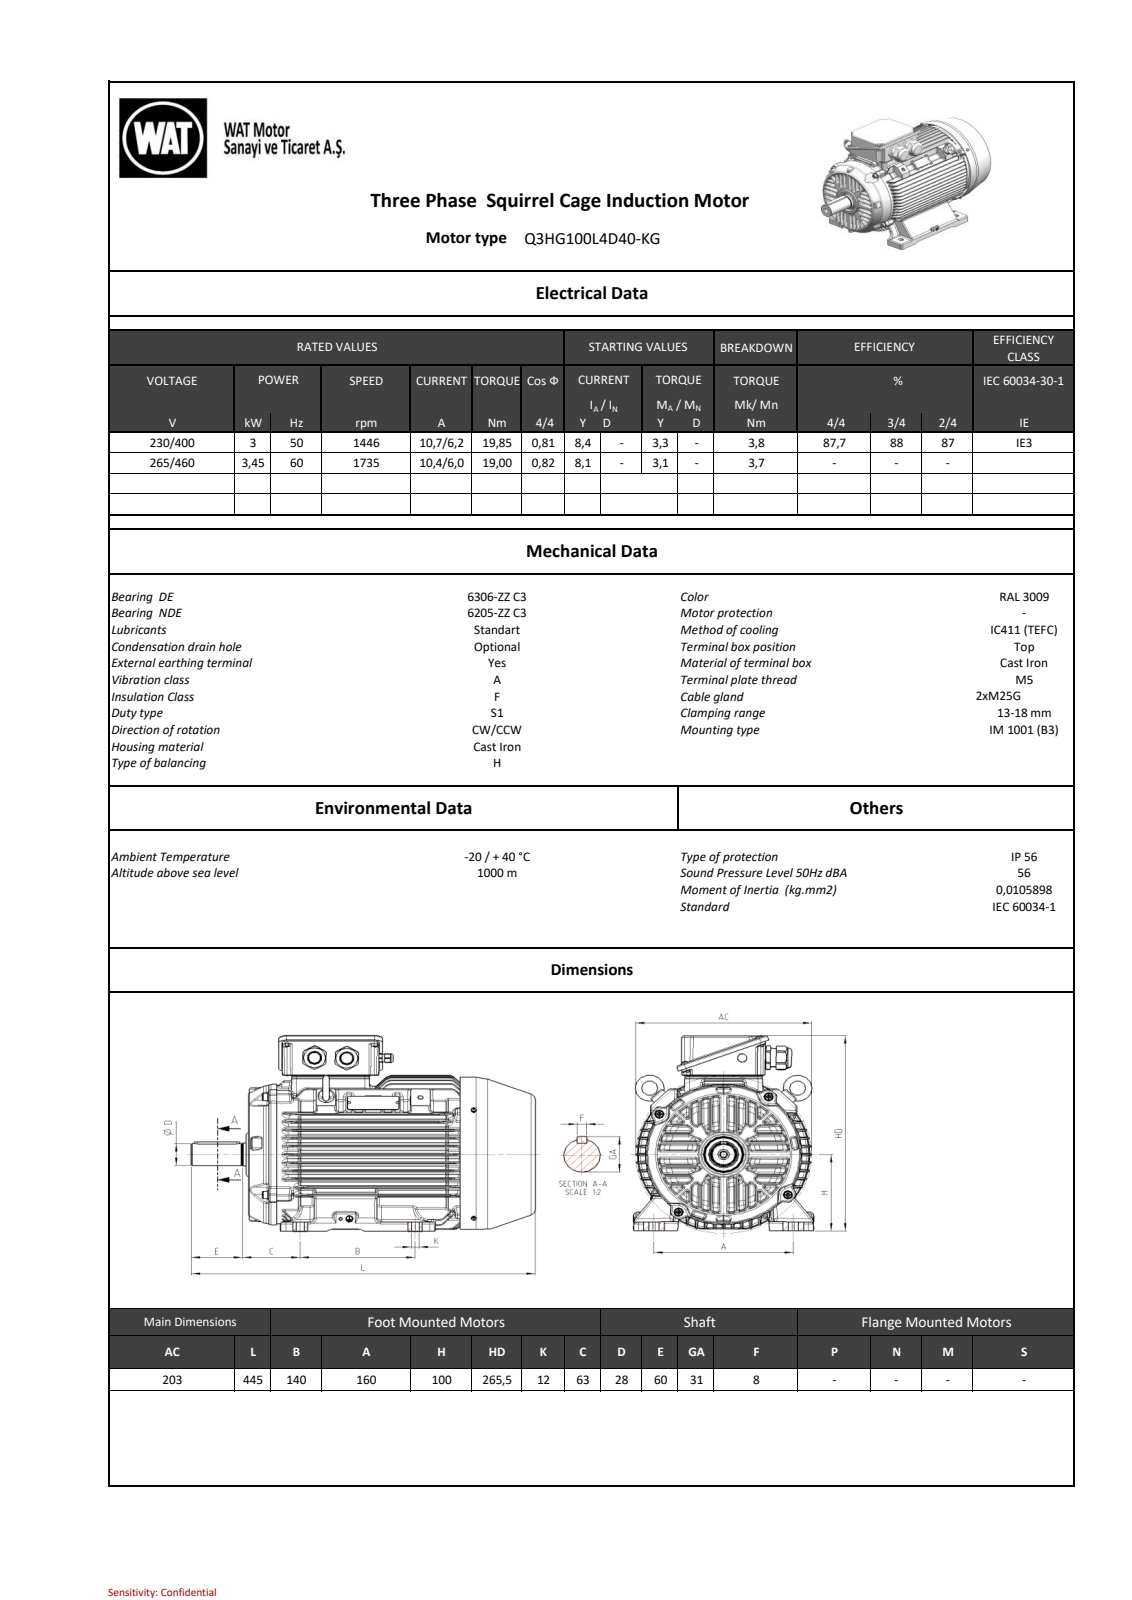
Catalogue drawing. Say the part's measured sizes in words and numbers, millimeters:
The part is named "C901A24426BAzd69". Its 3-D file was written by "SIEMENS PLM Software NX 11.0 (AUTOMOTIVE_DESIGN)". It is 0 solids with 4762 faces: 891 planar, 1250 cylindrical and 2621 other. Overall it measures 445 by 265.48 by 204.29 millimeters. Round holes: 8 of diameter 5, 3 of diameter 10, 2 of diameter 6.8, 2 of diameter 17.2, 1 of diameter 4.2, 1 of diameter 6.5, 1 of diameter 8.5, 1 of diameter 10.5, 1 of diameter 43.4, 1 of diameter 43.6, 1 of diameter 197. Round bosses or shafts: 4 of diameter 12, 4 of diameter 10, 4 of diameter 8.65, 4 of diameter 8, 4 of diameter 4, 2 of diameter 27.7, 2 of diameter 25.25, 2 of diameter 20. Partial cylindrical surfaces (rounded edges, fillets, slot ends): 372 of radius 3, 110 of radius 1.5, 70 of radius 2, 37 of radius 1, 32 of radius 1.8, 27 of radius 0.25, 12 of radius 5, 12 of radius 26.5. The main face-to-face distances are 13.52, 13.61, 27.13, 78.72, 51.59, 65.11, 40.83, 27.31, 13.7, 37.89. The hole center spacings are 89.5, 126.57, 31.07, 102.68, 146.62, 176.28, 179, 44.5.
